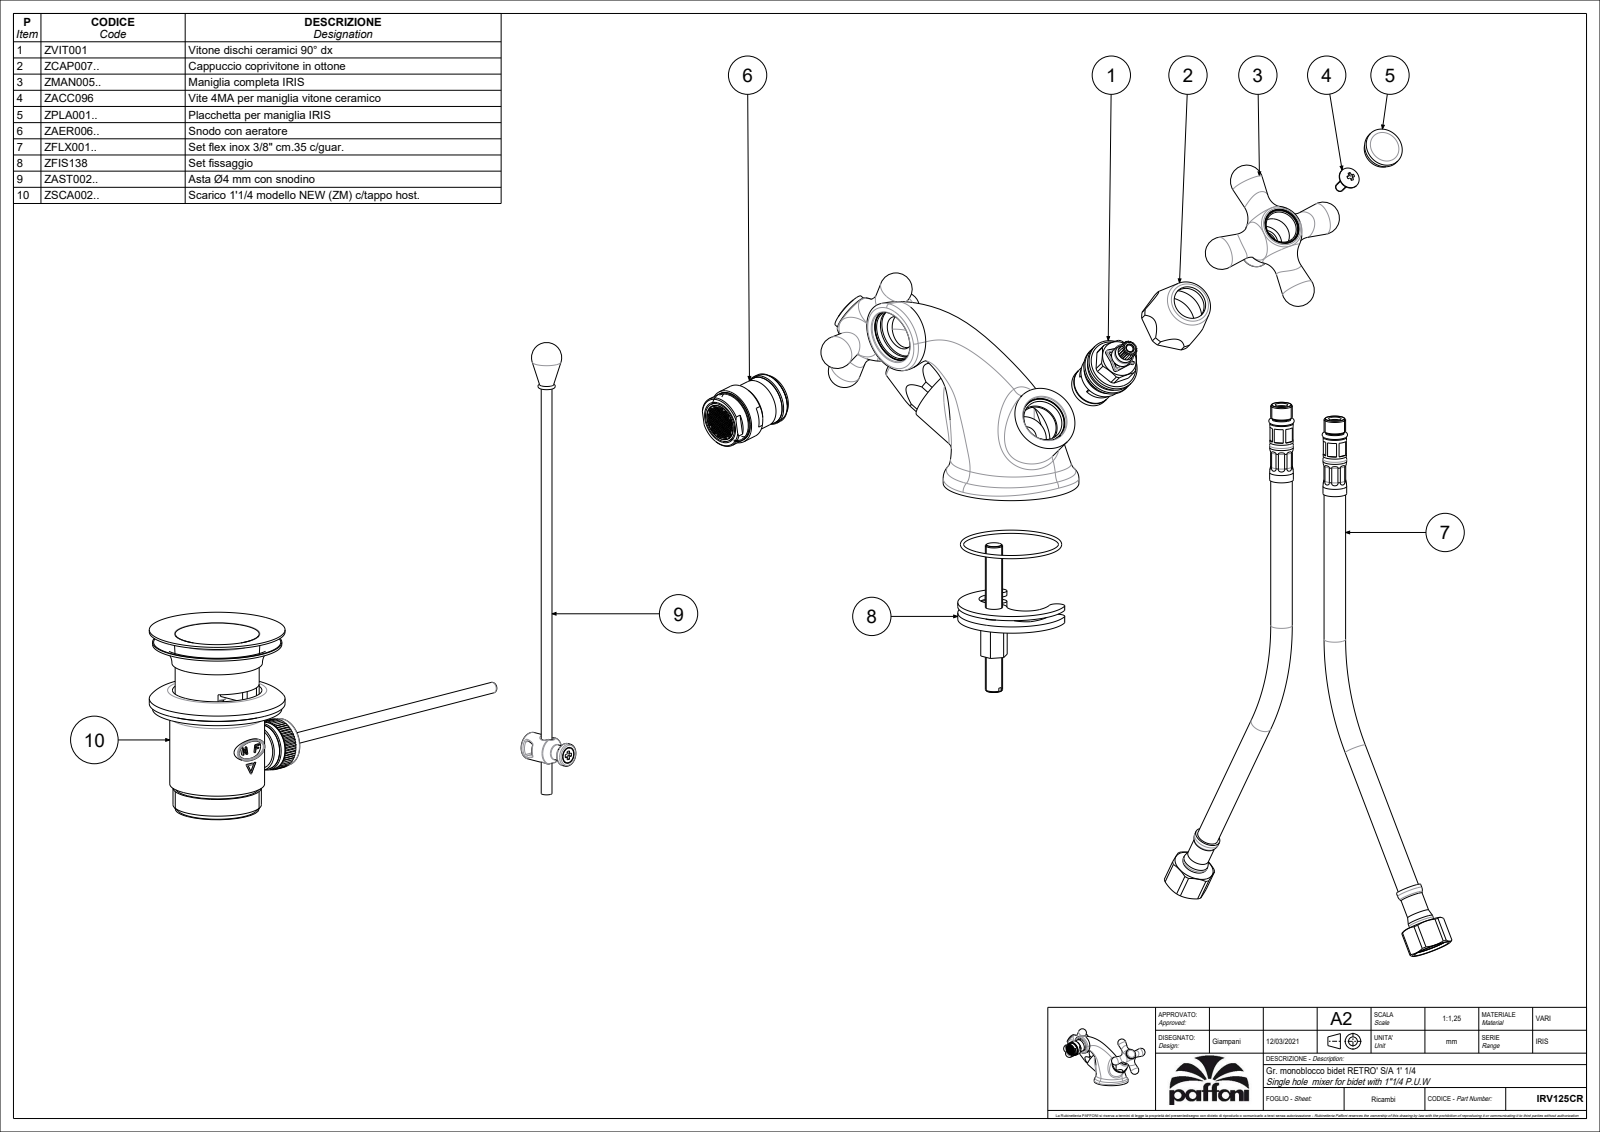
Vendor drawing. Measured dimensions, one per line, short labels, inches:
name: IRV125CR
written by: CREO PARAMETRIC BY PTC INC, 2020044 (CONFIG_CONTROL_DESIGN)
unit: in
bodies: 2 solids, 338 faces (84 planar, 85 cylindrical, 169 other)
size: 7.354 × 5.542 × 3.986
volume: 10.89 in³; area: 97.21 in²
holes: 4× ⌀0.354, 2× ⌀0.433, 2× ⌀0.827, 2× ⌀0.846, 1× ⌀0.217, 1× ⌀0.268, 1× ⌀0.315, 1× ⌀0.61, 1× ⌀0.65, 1× ⌀1.929
bosses: 2× ⌀1.102, 2× ⌀0.748, 2× ⌀0.709, 2× ⌀0.531, 1× ⌀2.48, 1× ⌀1.732, 1× ⌀1.016, 1× ⌀0.945
rounds: 2× R0.571, 1× R0.197
face distances: 0.335, 0.862, 1.13, 0.051, 0.283, 1.012, 0.119, 1.043, 0.948, 1.811
hole spacings: 0.295, 0.498, 0.531, 0.402, 0.441, 0.591, 0.843
